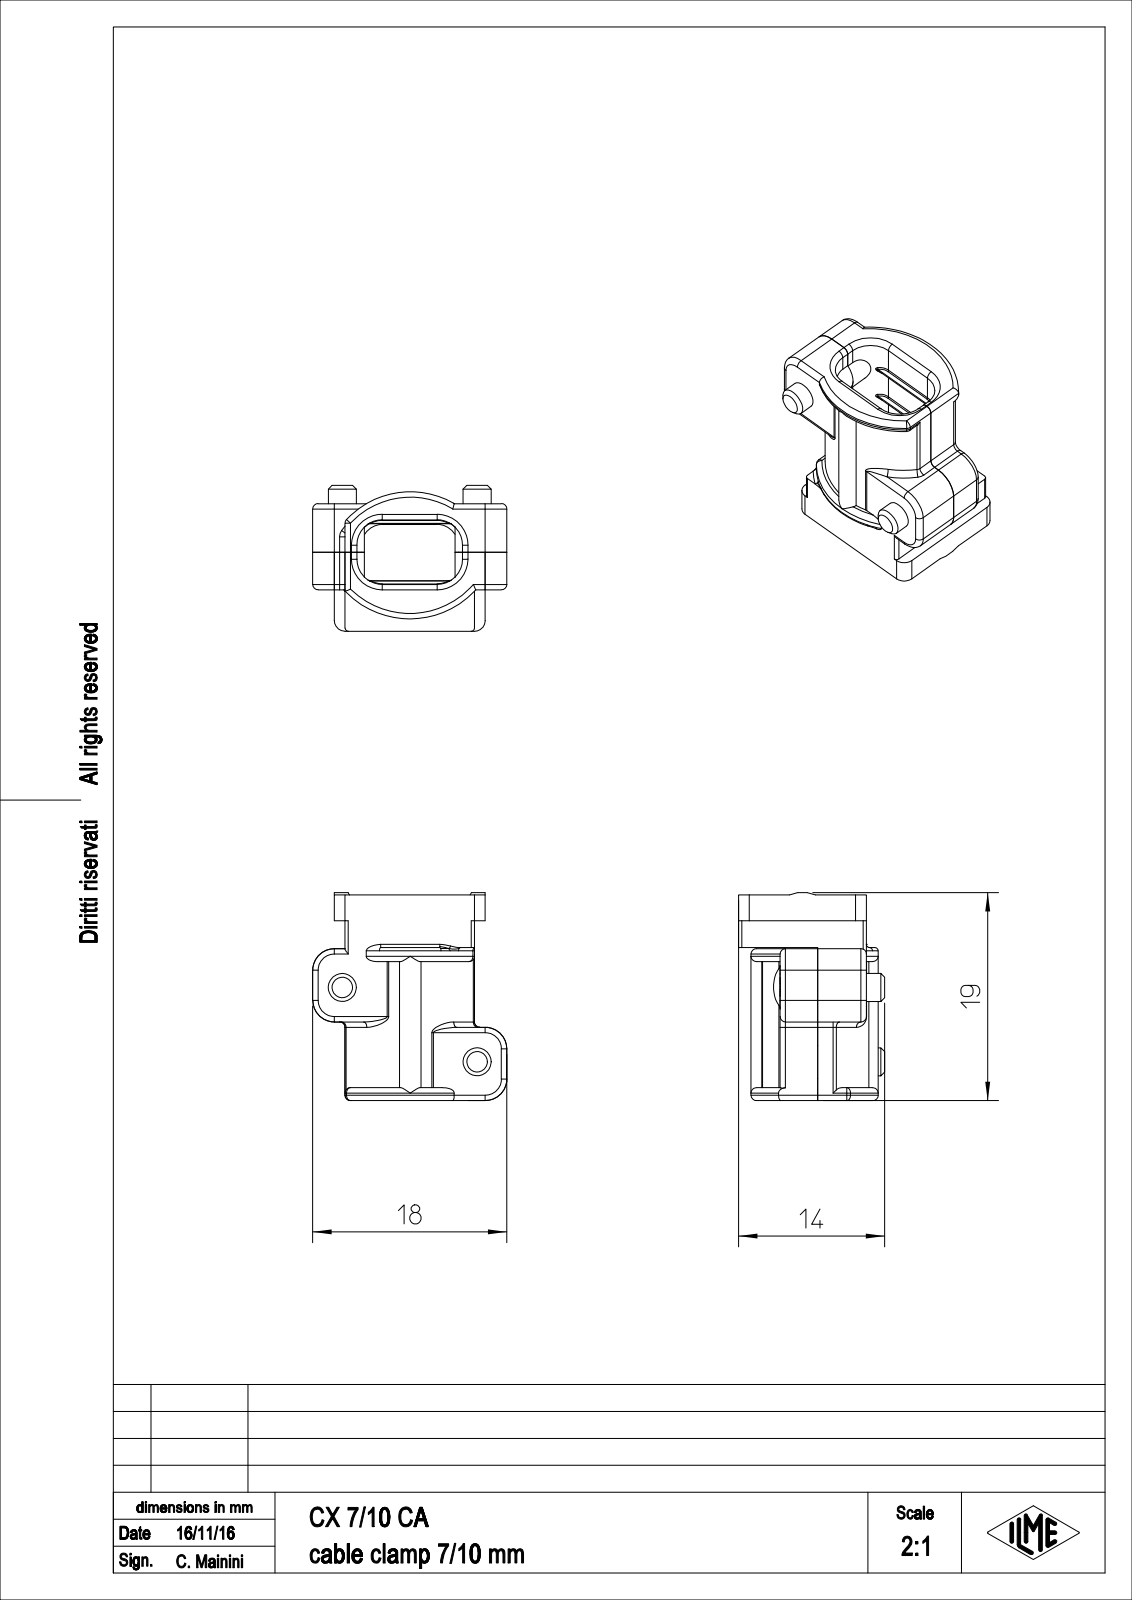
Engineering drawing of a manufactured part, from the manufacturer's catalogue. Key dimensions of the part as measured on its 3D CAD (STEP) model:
Part name (STEP PRODUCT): CX_7-10_CA
STEP written by: PTC Creo Elements/Direct Modeling 19.0E 27-Jun-2016 (C) Parametric Technology GmbH (AUTOMOTIVE_DESIGN)
Units: millimetres
Bodies: 1 solid, 422 faces (121 planar, 150 cylindrical, 151 other)
Overall size (bounding box): 19.3 × 18 × 13.55
Volume: 1 504 mm³ · Surface area: 1 935 mm²
Round holes (diameter × count): ⌀2.65 ×2
Round bosses / shafts (diameter × count): ⌀2.6 ×2, ⌀2.2 ×2
Partial cylindrical surfaces — rounded edges, fillets, slot ends (radius × count): R0.2 ×44, R0.5 ×39, R2 ×8, R0.1 ×6, R1 ×6, R0.3 ×5, R2.05 ×4, R2.35 ×4
Main face-to-face distances: 1.5, 12, 8, 11.85, 2.5, 13, 10.35, 6, 7.5, 4.35
Hole centre spacings: 14.33
